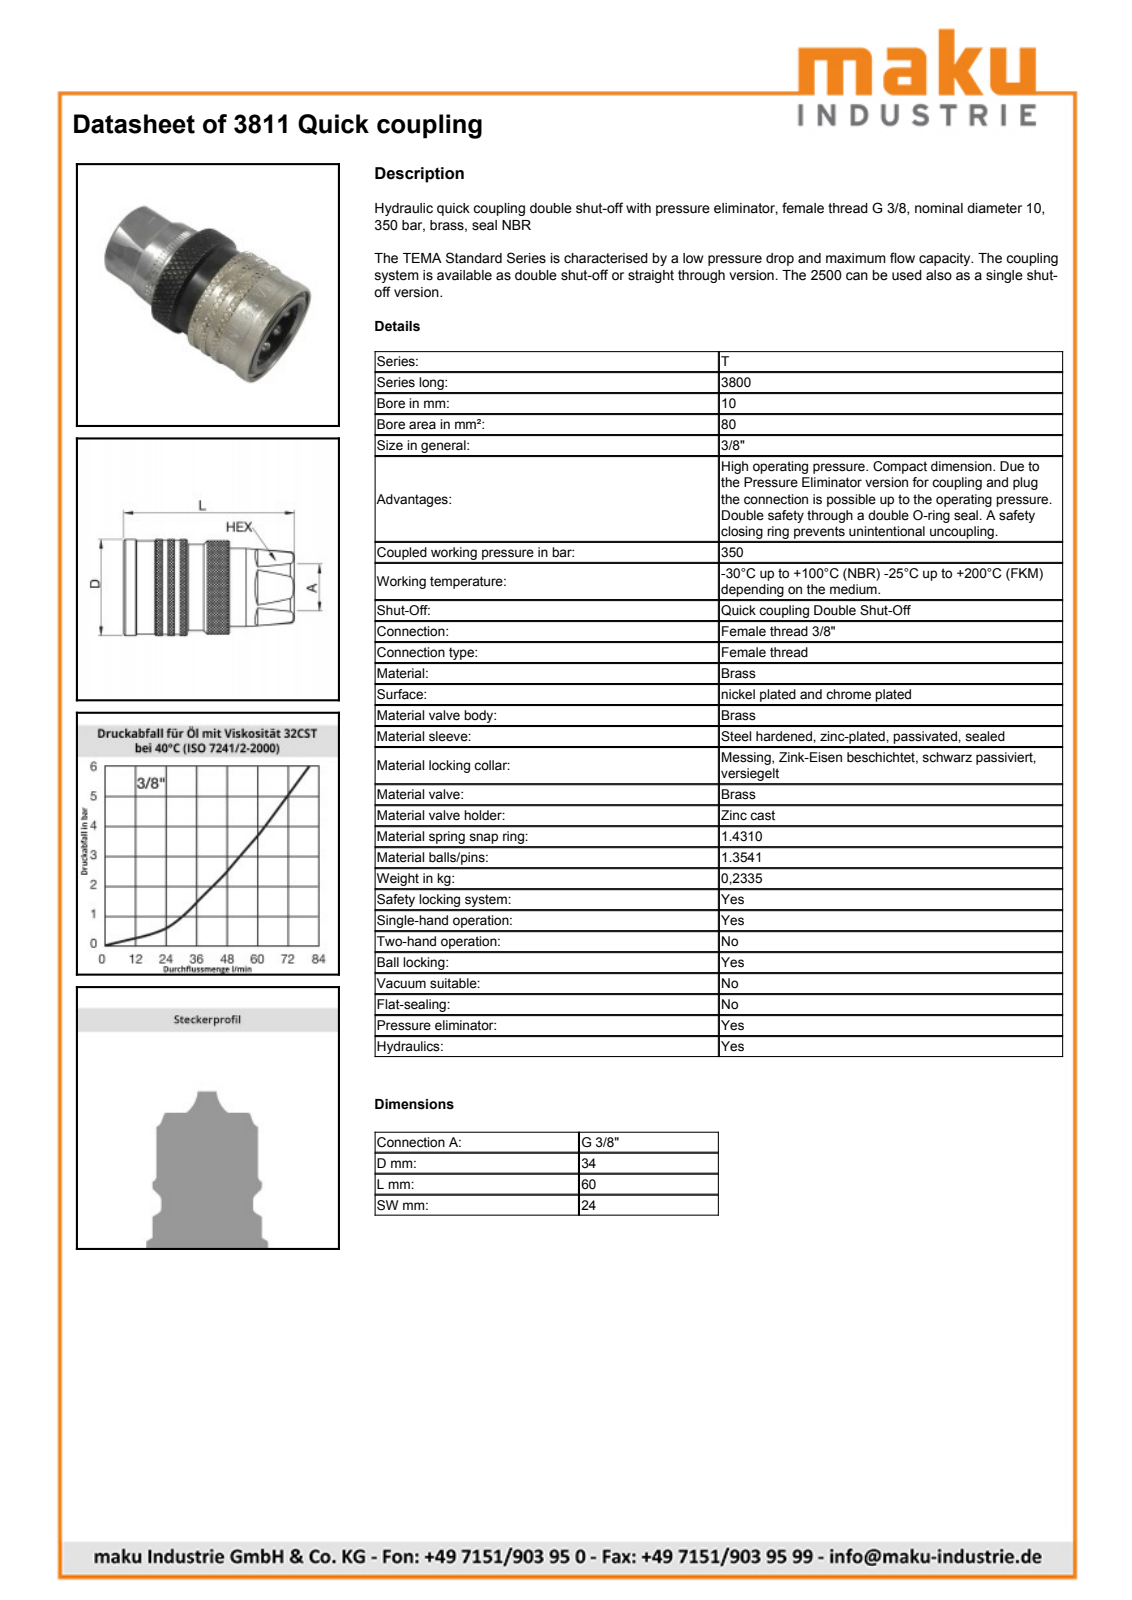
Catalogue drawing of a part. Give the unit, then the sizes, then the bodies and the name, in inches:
Units: inches
Overall size (bounding box): 2.37 × 1.339 × 1.339
Round holes (diameter × count): ⌀0.155 ×1, ⌀0.394 ×1, ⌀0.622 ×1, ⌀0.787 ×1, ⌀0.787 ×1, ⌀0.85 ×1, ⌀0.886 ×1, ⌀0.963 ×1, ⌀0.964 ×1, ⌀1.165 ×1, ⌀1.228 ×1
Round bosses / shafts (diameter × count): ⌀1.339 ×1, ⌀1.307 ×1, ⌀1.299 ×1, ⌀1.205 ×1, ⌀1.197 ×1, ⌀1.087 ×1
Main face-to-face distances: 0.945, 0.866, 0.535, 0.571, 1.437, 2.362, 1.791, 0.925, 0.103, 0.902
Volume: 1.989 in³ · Surface area: 17.44 in²
Bodies: 1 solid, 143 faces (35 planar, 46 cylindrical, 62 other)
Part name (STEP PRODUCT): 3811
STEP written by: SolidWorks 2009 (AUTOMOTIVE_DESIGN)
